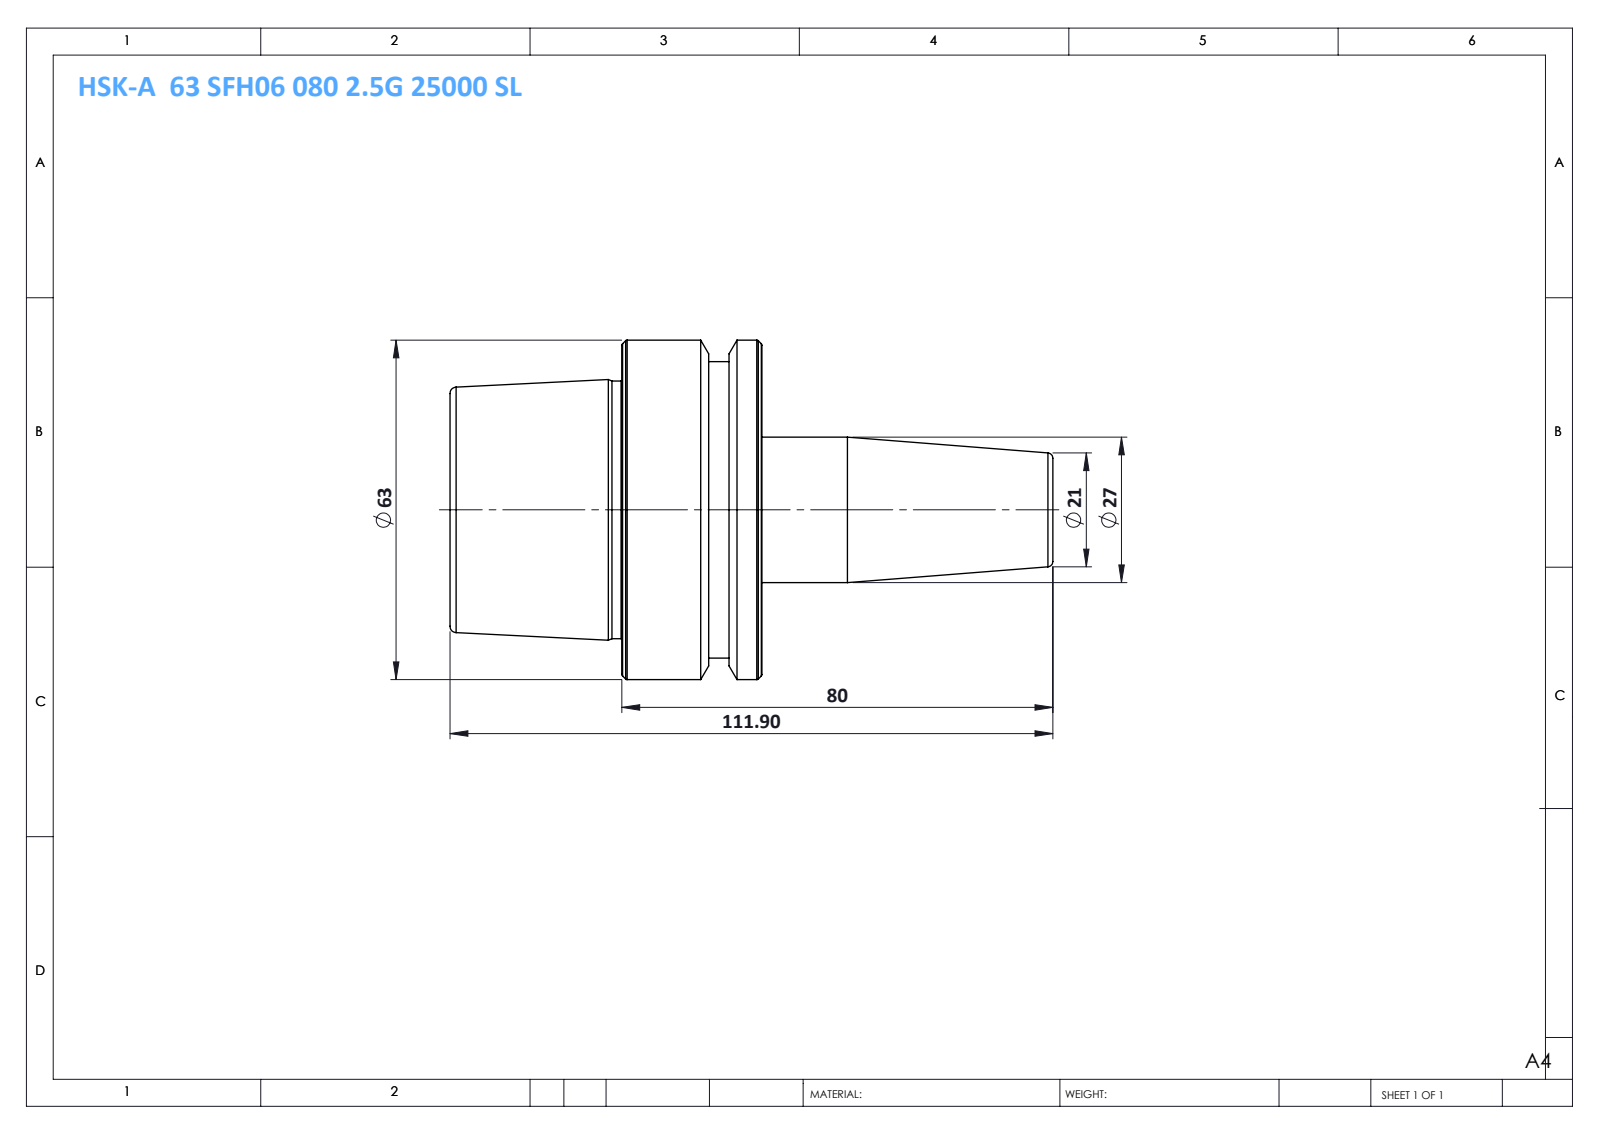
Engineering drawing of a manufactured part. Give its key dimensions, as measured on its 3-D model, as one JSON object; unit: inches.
{"part_name": "HSK-A 63 SFH06 080 2.5G 25000 SL", "step_written_by": "SolidWorks 2014 (CONFIG_CONTROL_DESIGN)", "units": "inches", "bodies": {"solids": 1, "faces": 46, "planar": 6, "cylindrical": 10, "other": 30}, "overall_size": [4.406, 2.48, 2.48], "volume_in3": 9.704, "surface_area_in2": 31.98, "round_bosses_or_shafts": [[2.48, 1], [2.165, 1], [1.881, 1], [1.063, 1]], "face_to_face_distances": [2.28, 1.024, 1.256, 2.126, 3.15, 4.406, 2.366, 0.24, 0.783, 2.039]}
